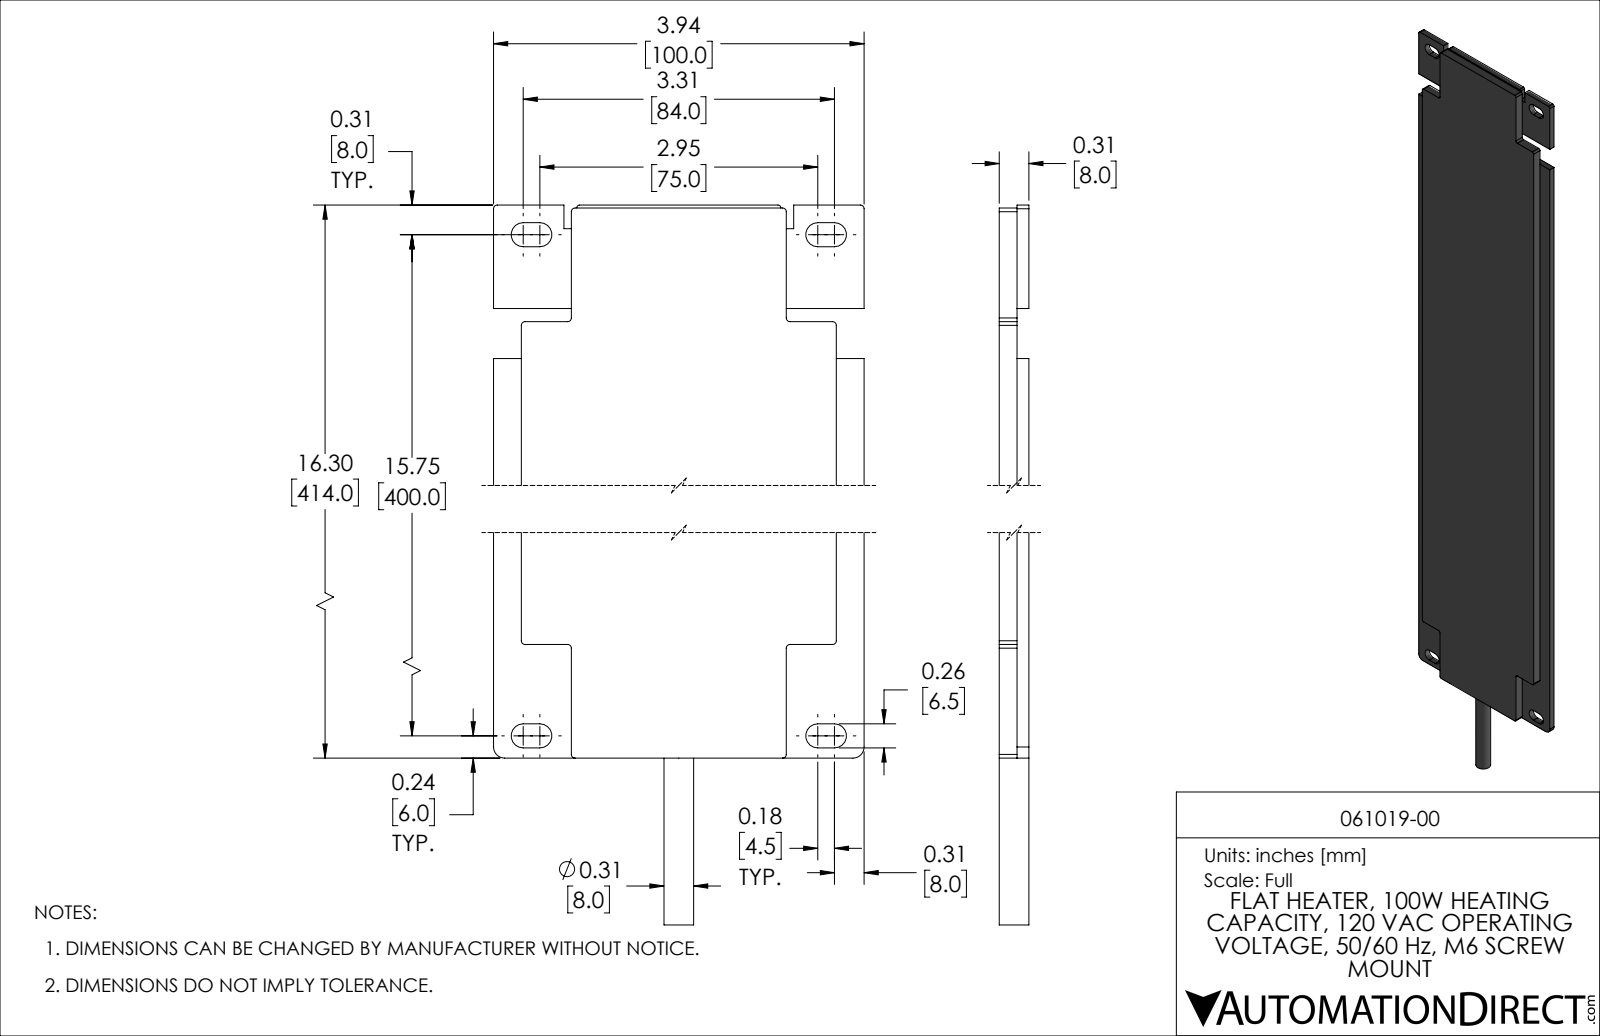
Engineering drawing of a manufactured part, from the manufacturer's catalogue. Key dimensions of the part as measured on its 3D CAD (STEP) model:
Part name (STEP PRODUCT): 061019-00
STEP written by: SolidWorks 2019 (AUTOMOTIVE_DESIGN)
Units: inches
Bodies: 1 solid, 75 faces (48 planar, 27 cylindrical, 0 other)
Overall size (bounding box): 18.071 × 3.937 × 0.315
Volume: 17.7 in³ · Surface area: 142.3 in²
Round bosses / shafts (diameter × count): ⌀0.315 ×1
Partial cylindrical surfaces — rounded edges, fillets, slot ends (radius × count): R0.039 ×14, R0.128 ×8, R0.031 ×2, R0.118 ×2
Main face-to-face distances: 0.315, 0.189, 0.126, 0.295, 3.642, 3.346, 3.937, 0.827, 3.11, 0.531
